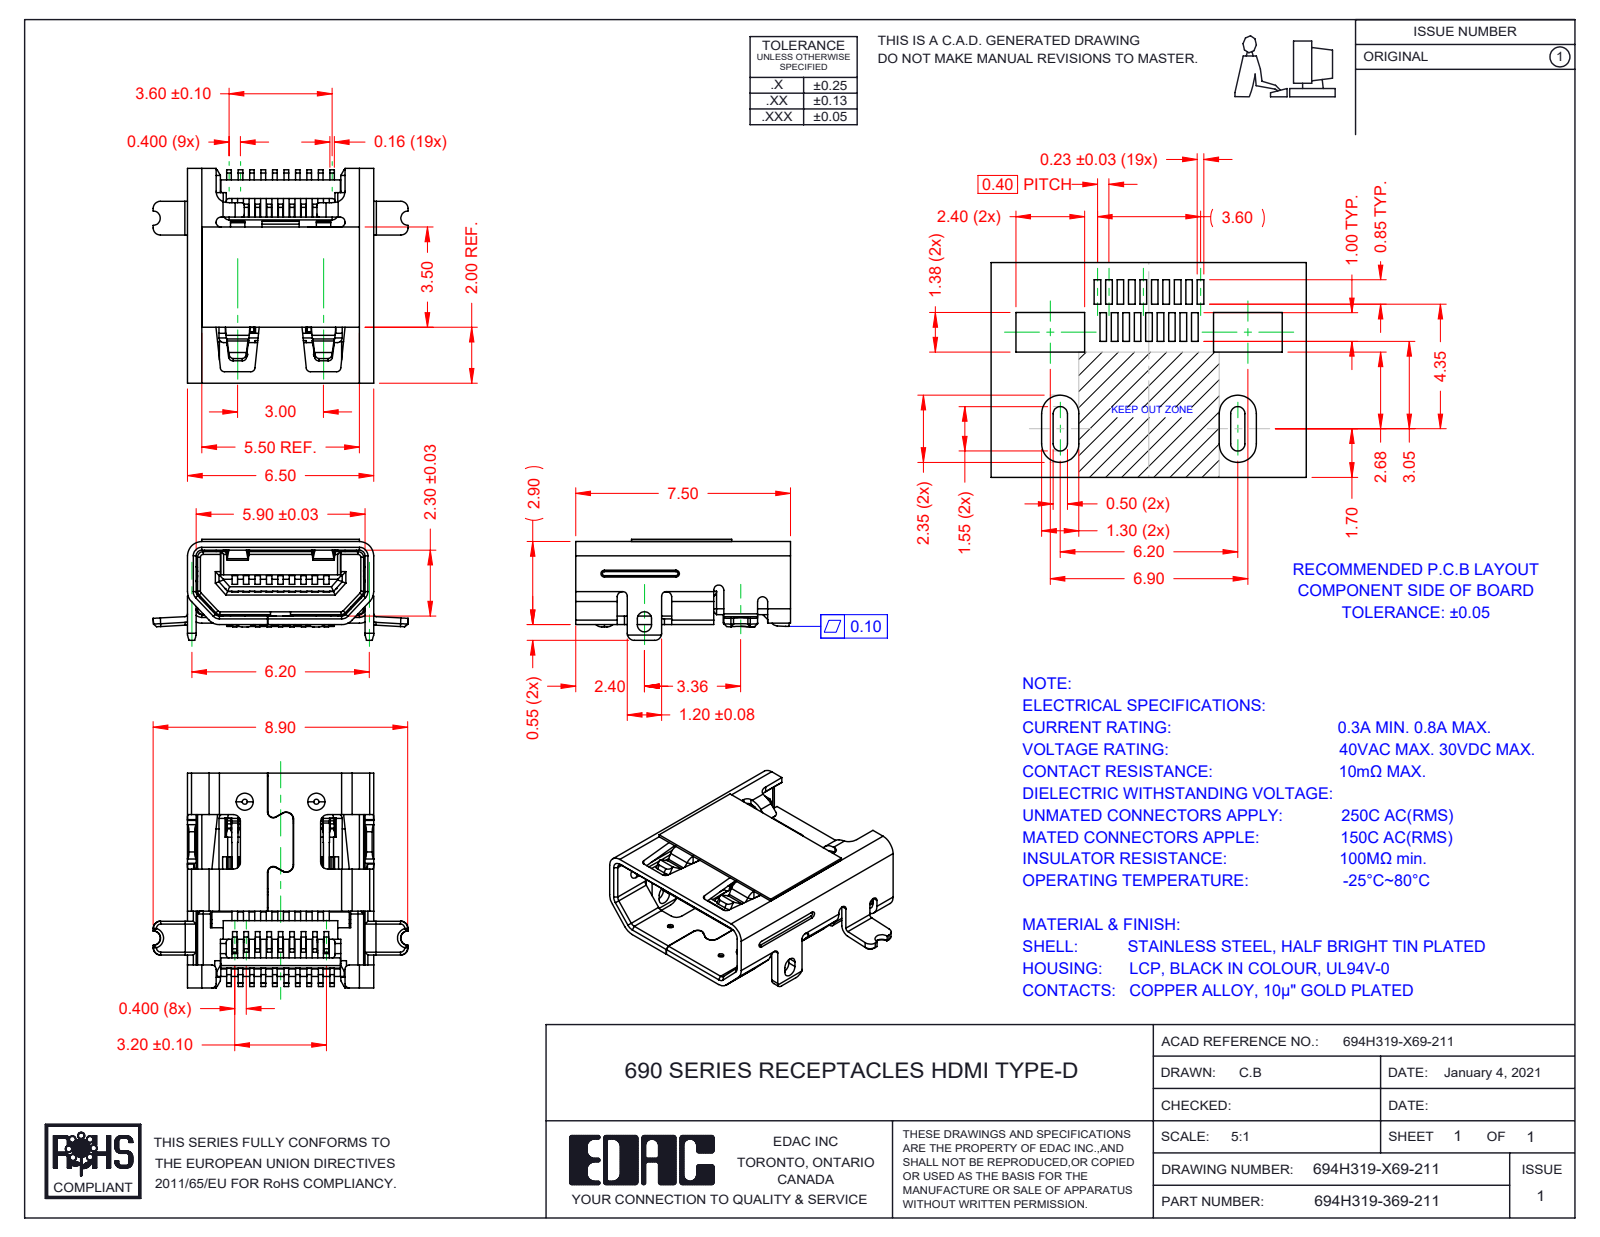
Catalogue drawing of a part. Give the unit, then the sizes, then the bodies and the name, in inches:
Units: inches
Overall size (bounding box): 0.35 × 0.295 × 0.139
Round holes (diameter × count): ⌀0.008 ×2
Partial cylindrical surfaces — rounded edges, fillets, slot ends (radius × count): R0.006 ×27, R0.008 ×18, R0.01 ×16, R0.004 ×10, R0.02 ×8, R0.006 ×6, R0.007 ×6, R0.014 ×6
Main face-to-face distances: 0.102, 0.014, 0.091, 0.244, 0.114, 0.026, 0.015, 0.106, 0.117, 0.02
Hole centre spacings: 0.098
Volume: 0.004 in³ · Surface area: 0.711 in²
Bodies: 3 solids, 1453 faces (1130 planar, 217 cylindrical, 106 other)
Part name (STEP PRODUCT): Shell 694H319-X69-211; Tape 694H319-X69-211; 694H319-169-211; Insulator 694H319-X69-211
STEP written by: SolidWorks 2020 (AUTOMOTIVE_DESIGN)
